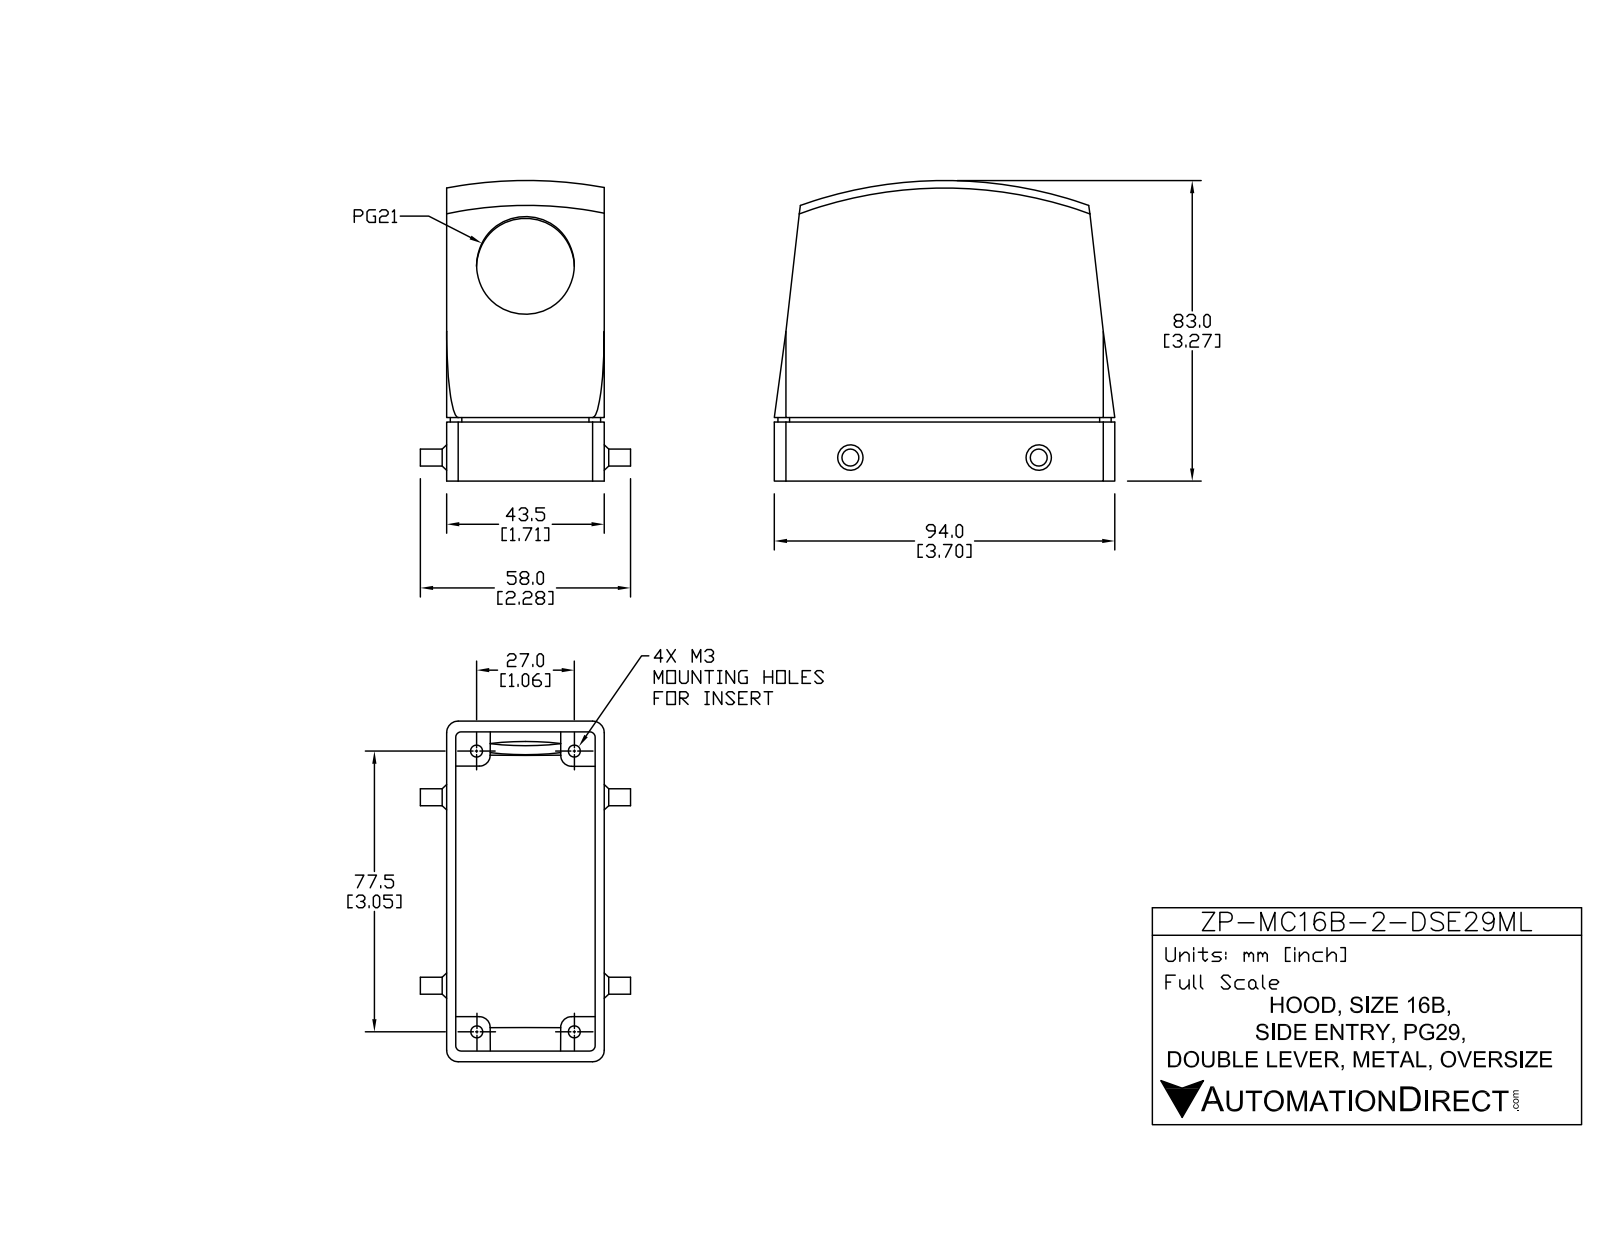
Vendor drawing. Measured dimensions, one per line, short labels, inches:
name: ZP-MC16B-2-DSE29ML
written by: SolidWorks 2011 (AUTOMOTIVE_DESIGN)
unit: in
bodies: 9 solids, 104 faces (60 planar, 34 cylindrical, 10 other)
size: 3.701 × 3.053 × 2.283
volume: 3.958 in³; area: 78.58 in²
holes: 4× ⌀0.138, 1× ⌀1.378
bosses: 2× ⌀0.184
rounds: 8× R0.126, 4× R0.059, 4× R0.118, 1× R0.028
face distances: 0.098, 1.614, 1.713, 1.516, 0.374, 0.117, 3.584, 3.094, 3.21, 0.491
hole spacings: 1.14, 3.13, 3.331
